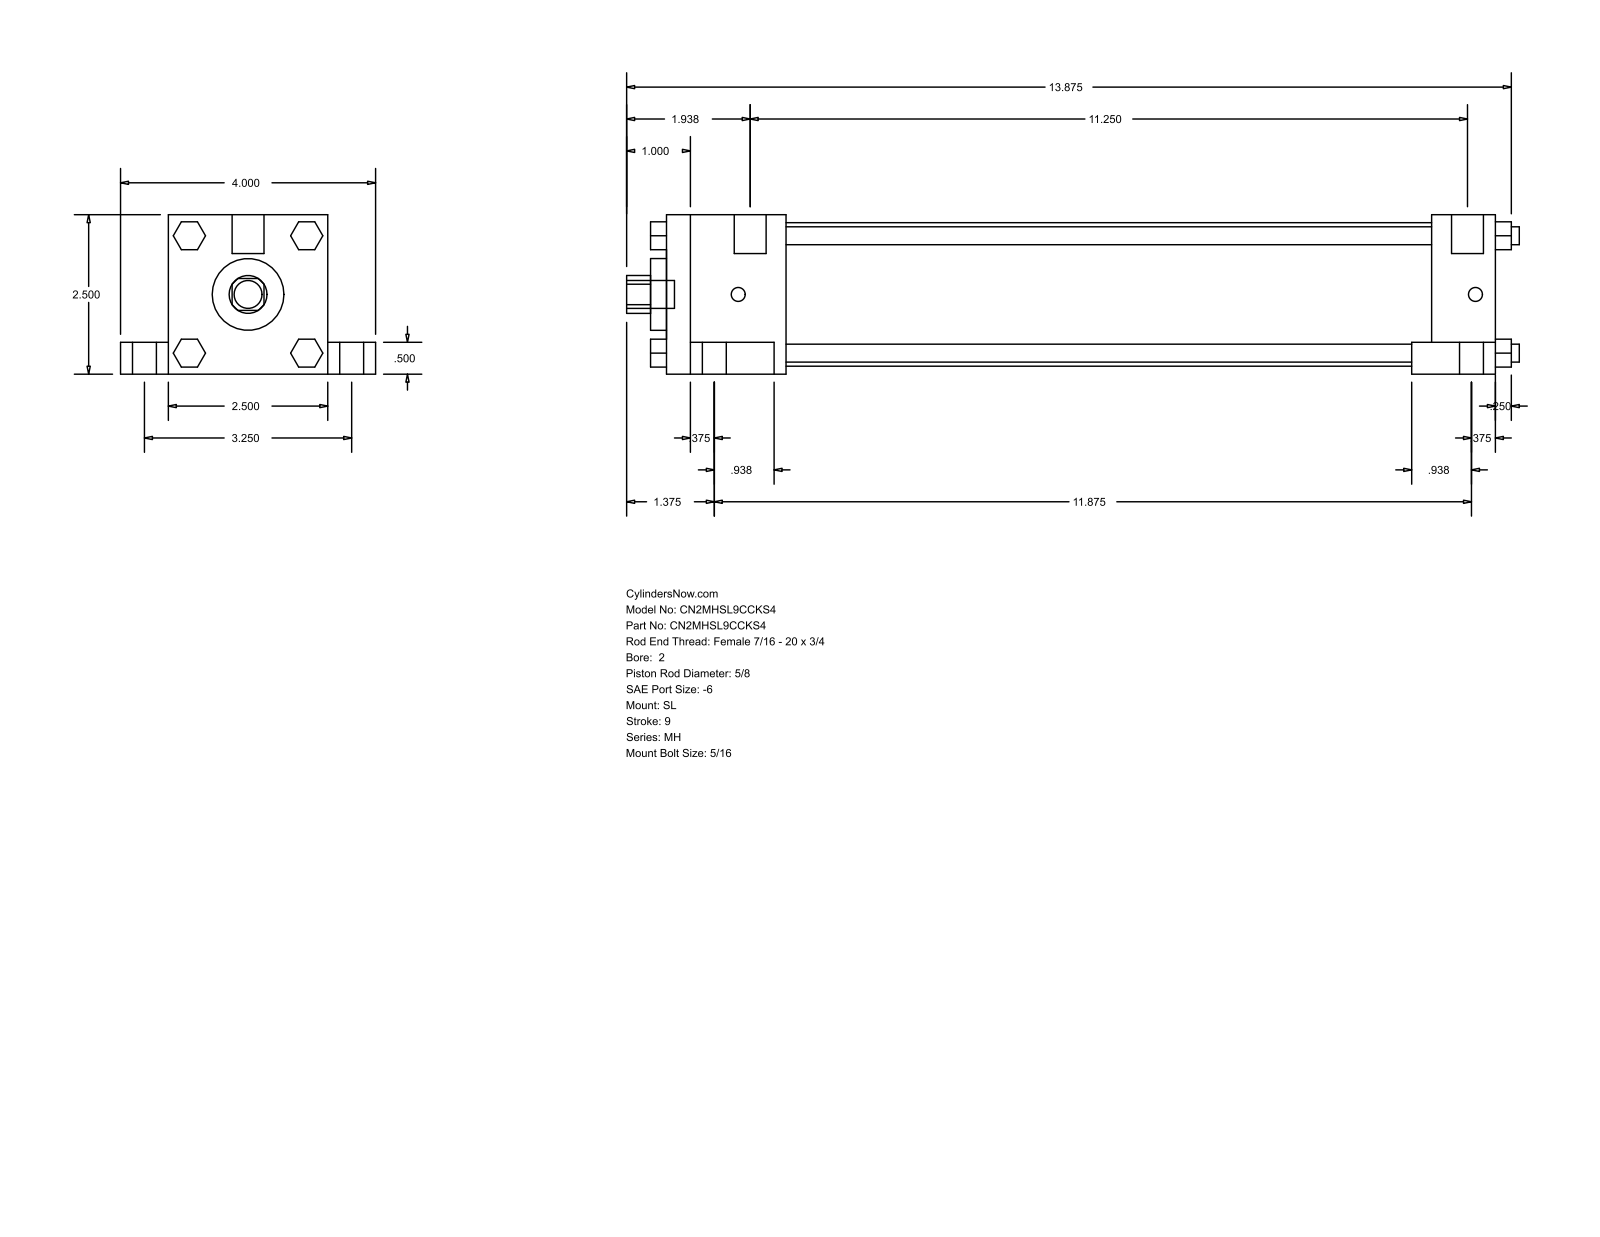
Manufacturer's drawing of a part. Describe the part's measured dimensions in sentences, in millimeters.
The part is named "MH_SL__0200_0.625". Its 3-D file was written by "GSSL Pune (CONFIG_CONTROL_DESIGN)". It is 0 solids with 148 faces: 112 planar, 36 cylindrical and 0 other. Overall it measures 355.6 by 101.6 by 63.5 millimeters. Round holes: 1 of diameter 15.88, 1 of diameter 28.57, 1 of diameter 57.15. Round bosses or shafts: 4 of diameter 15.88, 4 of diameter 9.53, 4 of diameter 7.14, 4 of diameter 5.56, 2 of diameter 12.7, 1 of diameter 11.11. Partial cylindrical surfaces (rounded edges, fillets, slot ends): 1 of radius 7.54. The main face-to-face distances are 63.5, 330.19, 12.7, 19.05, 50.8, 82.55, 304.8, 25.39, 47.62, 257.18.
